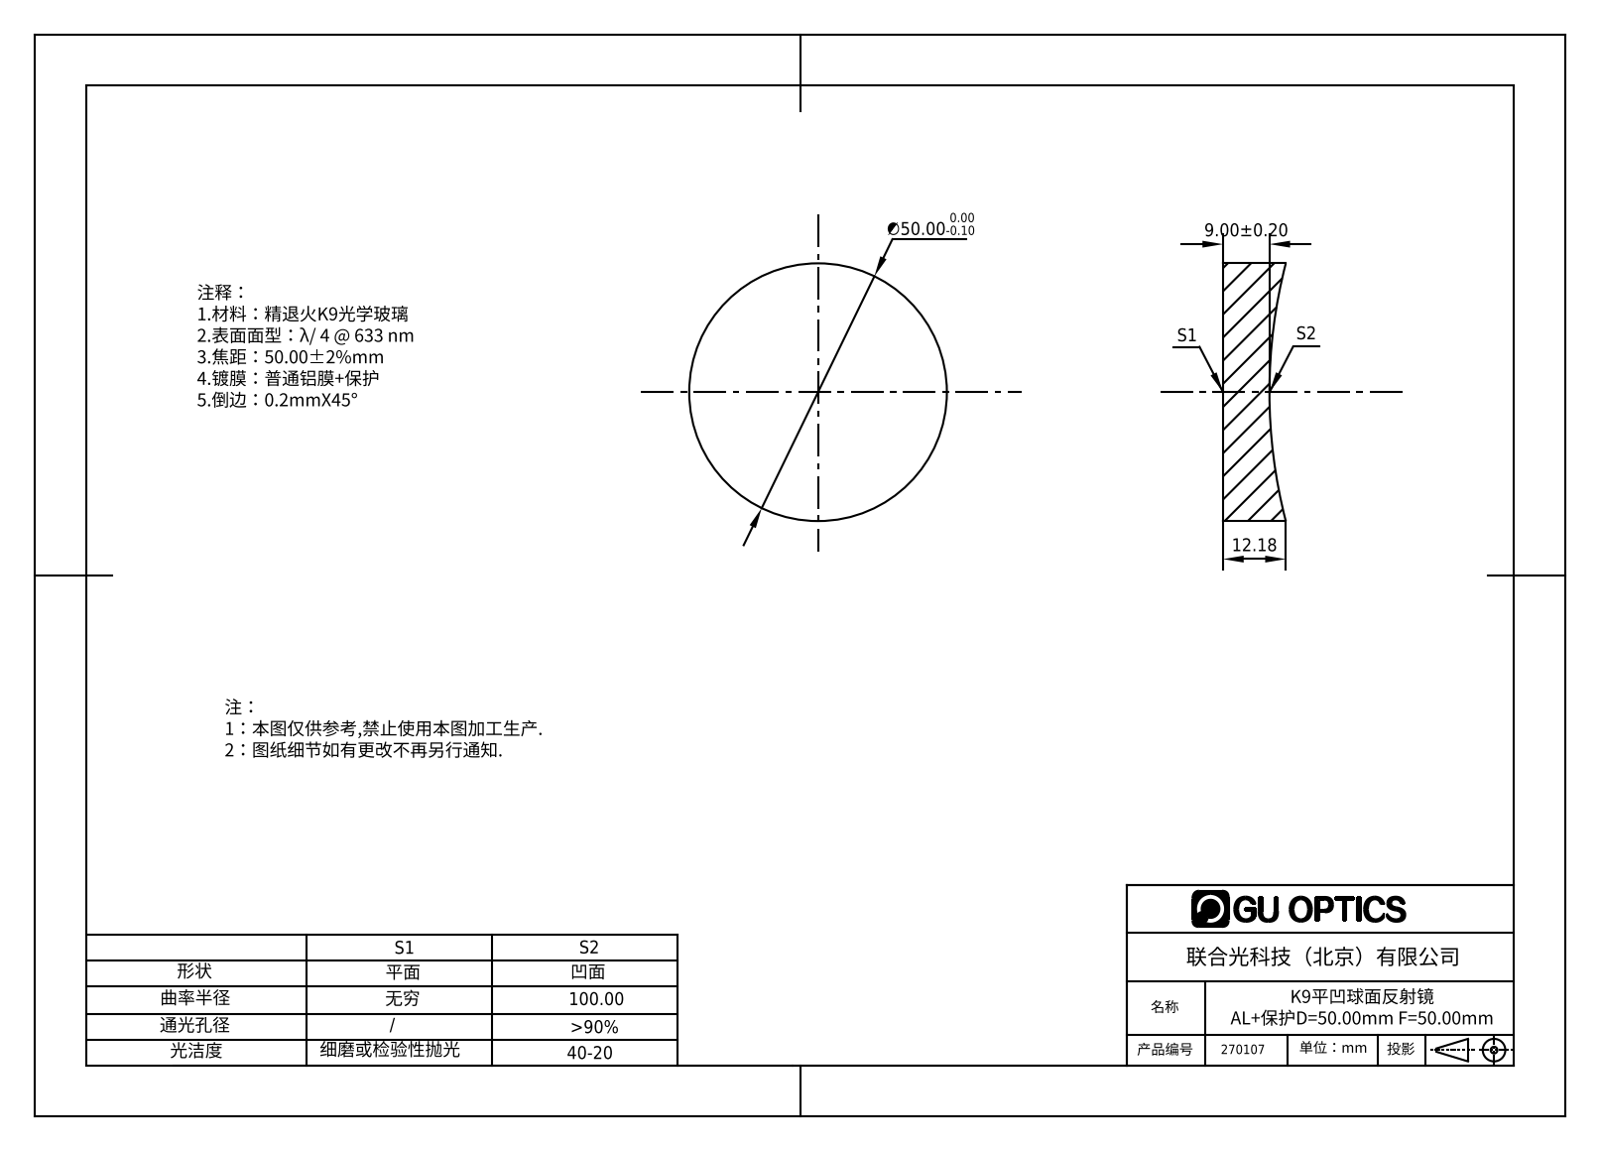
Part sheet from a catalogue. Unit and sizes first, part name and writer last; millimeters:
Units: millimetres
Overall size (bounding box): 50 × 50 × 12.18
Round bosses / shafts (diameter × count): ⌀50 ×1
Volume: 20 772 mm³ · Surface area: 5 871 mm²
Bodies: 1 solid, 5 faces (1 planar, 2 cylindrical, 2 other)
Part name (STEP PRODUCT): 270042
STEP written by: SolidWorks 2016 (AUTOMOTIVE_DESIGN)
